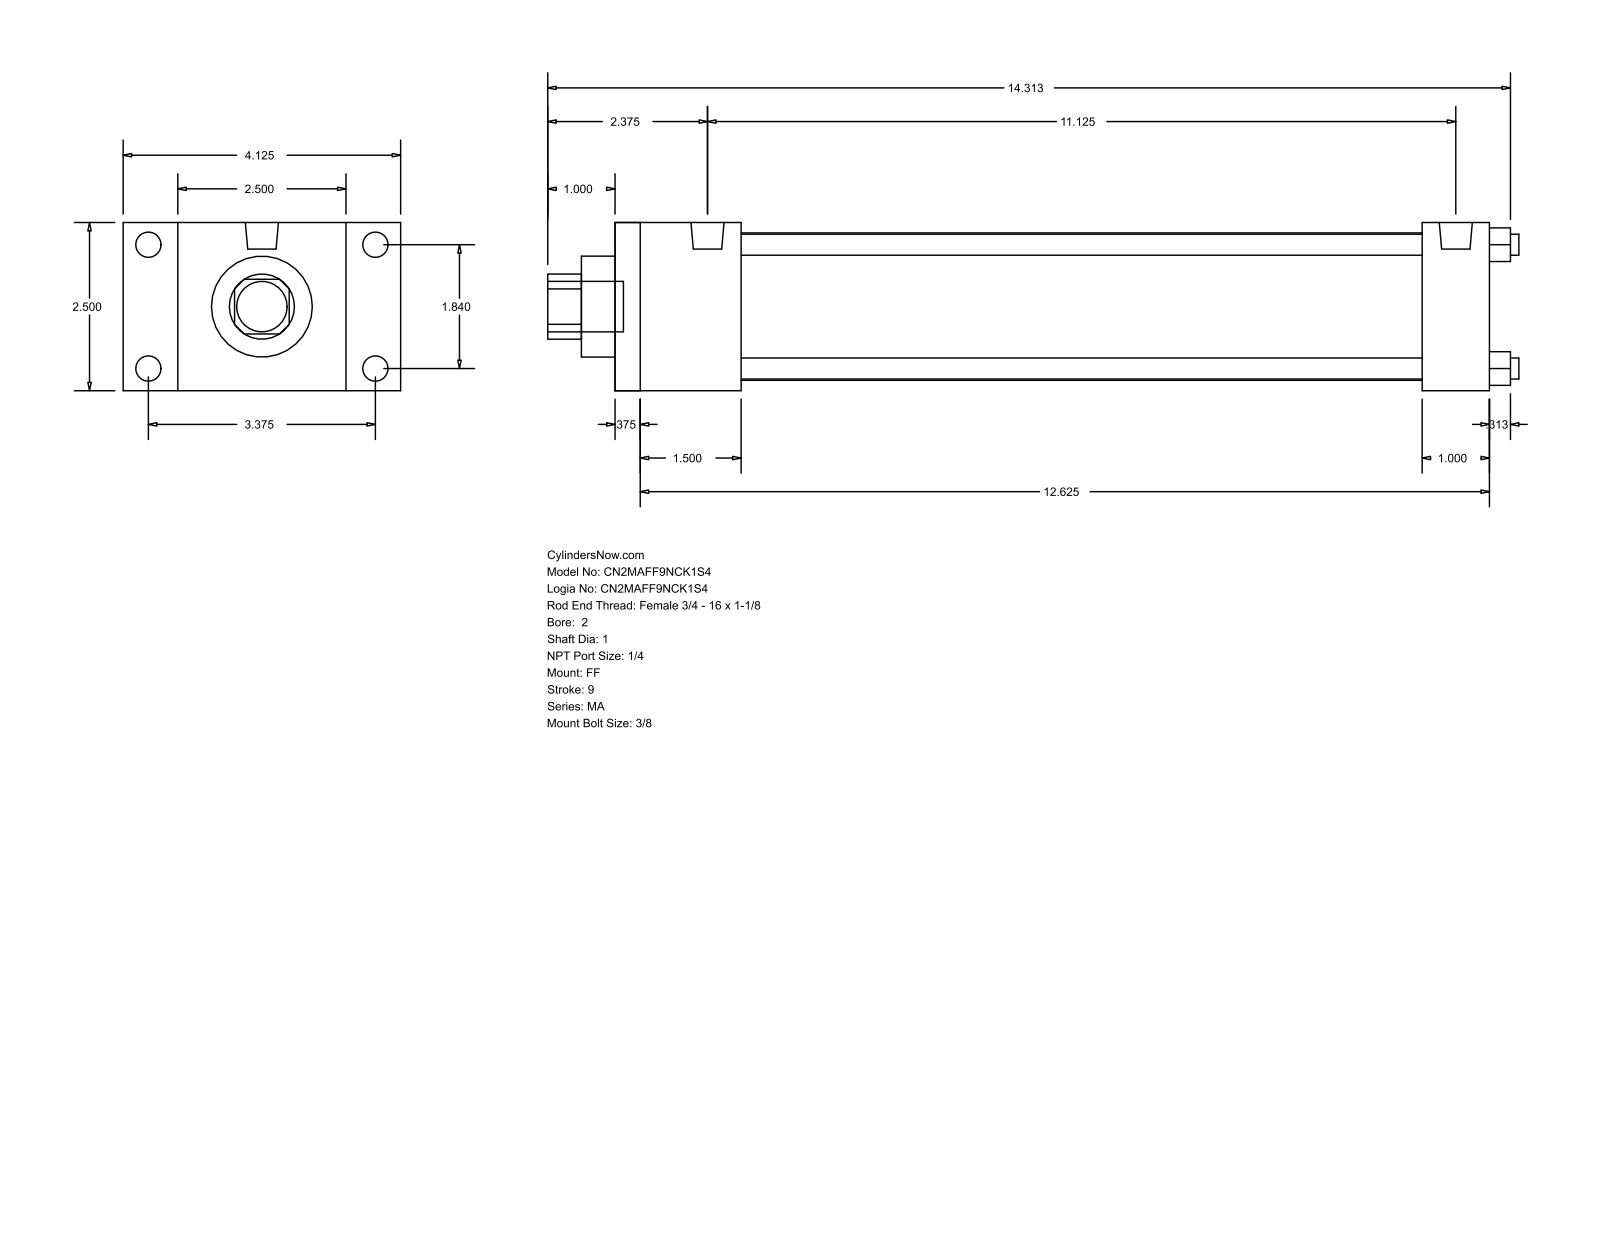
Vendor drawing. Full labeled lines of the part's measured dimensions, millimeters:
Part name (STEP PRODUCT): MA_FF__0200_1
STEP written by: GSSL Pune (CONFIG_CONTROL_DESIGN)
Units: millimetres
Bodies: 0 solids, 92 faces (64 planar, 28 cylindrical, 0 other)
Overall size (bounding box): 366.71 × 104.78 × 63.5
Round holes (diameter × count): ⌀7.94 ×4, ⌀25.4 ×1, ⌀38.1 ×1, ⌀55.63 ×1
Round bosses / shafts (diameter × count): ⌀9.53 ×4, ⌀7.94 ×4, ⌀12.49 ×2, ⌀19.05 ×1
Partial cylindrical surfaces — rounded edges, fillets, slot ends (radius × count): R12.29 ×1
Main face-to-face distances: 63.5, 330.2, 9.52, 320.68, 25.4, 20.64, 12.7, 47.63, 304.8, 38.11
Hole centre spacings: 33.05, 46.74, 66.1
